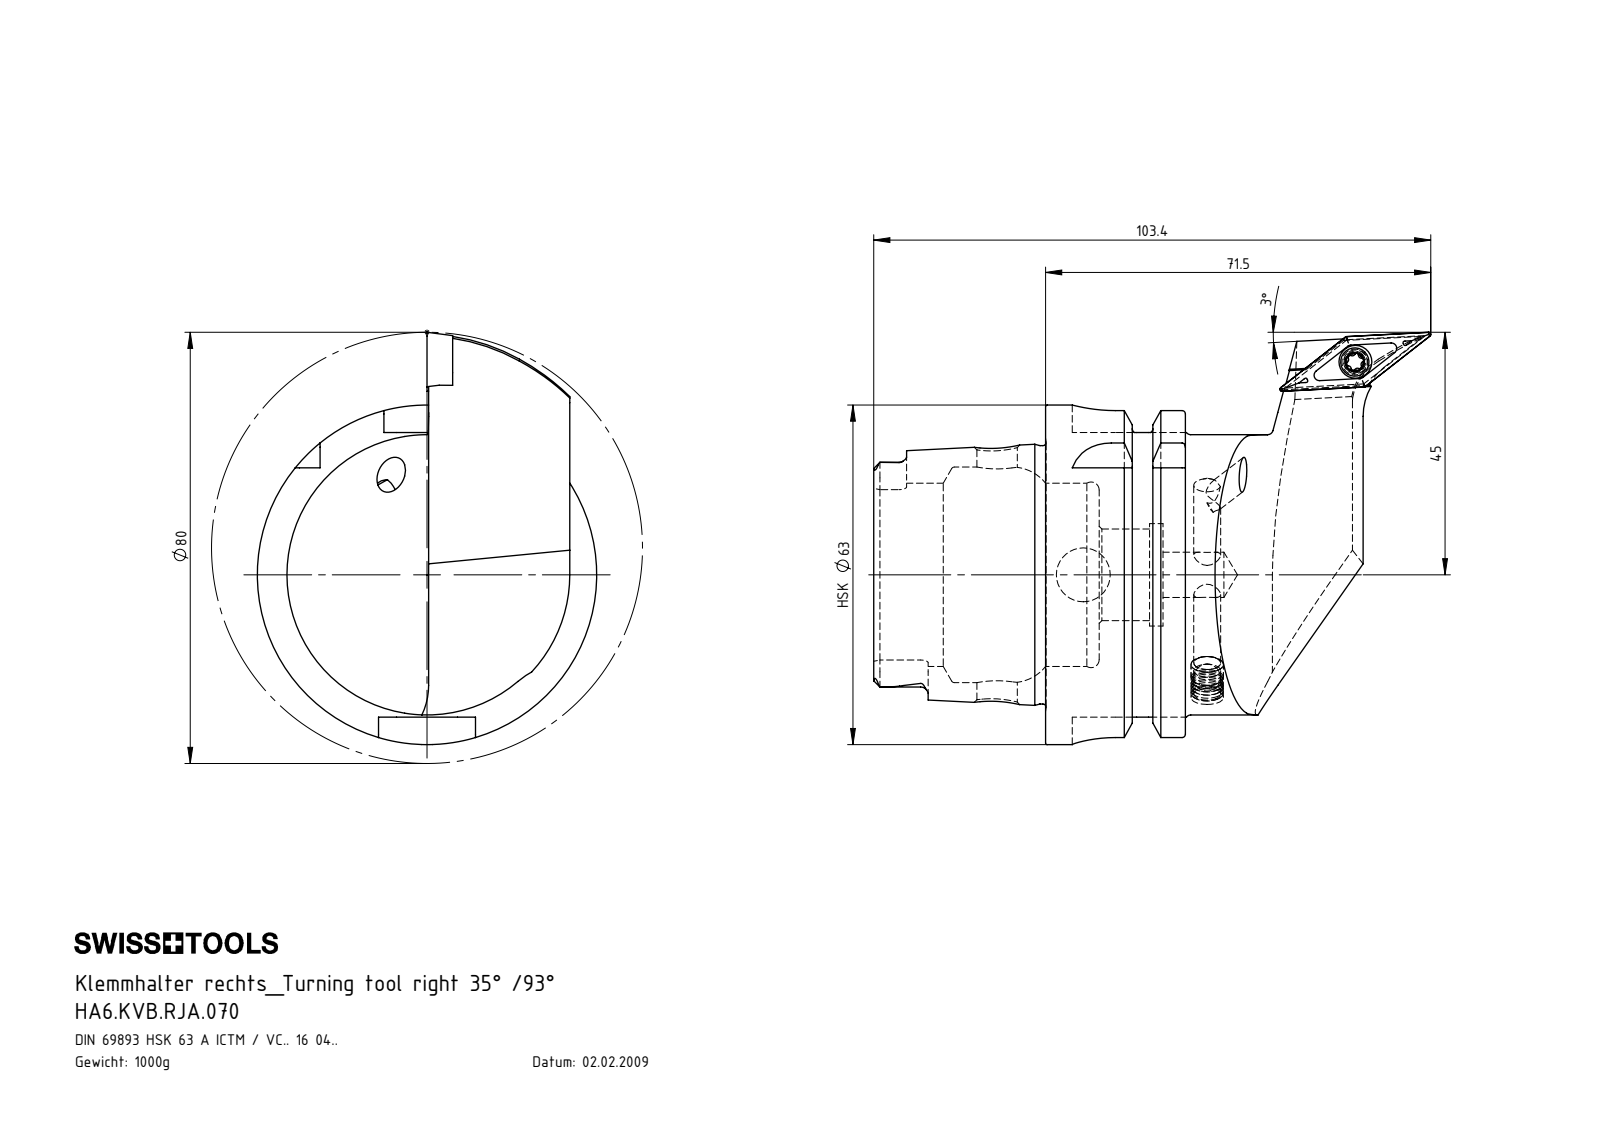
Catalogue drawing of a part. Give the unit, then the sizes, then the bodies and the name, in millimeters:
Units: millimetres
Overall size (bounding box): 103.4 × 76.5 × 63
Round holes (diameter × count): ⌀5 ×3, ⌀3.3 ×1, ⌀4.4 ×1, ⌀6 ×1, ⌀6.1 ×1, ⌀7.5 ×1, ⌀8.4 ×1, ⌀10 ×1, ⌀17 ×1, ⌀19 ×1, ⌀34 ×1, ⌀40 ×1
Round bosses / shafts (diameter × count): ⌀63 ×1, ⌀54.95 ×1, ⌀52 ×1, ⌀47.94 ×1, ⌀6 ×1, ⌀5.25 ×1, ⌀4 ×1
Partial cylindrical surfaces — rounded edges, fillets, slot ends (radius × count): R0.34 ×6, R0.59 ×6, R1.4 ×6, R8 ×4, R2.82 ×2, R2.88 ×2, R6 ×1, R11 ×1
Main face-to-face distances: 25.95, 16, 9.95, 26.2, 31.9, 41.85, 57.85, 52.8, 21.8, 11.85
Hole centre spacings: 64.02, 64.13
Volume: 126 907 mm³ · Surface area: 29 586 mm²
Bodies: 5 solids, 317 faces (82 planar, 90 cylindrical, 145 other)
Part name (STEP PRODUCT): VCMT160404; HA6.KVB.RJA.070; WCB-ER2.001.009_A; HA6-KVB.RJA.070_B (+1 more)
STEP written by: SolidWorks 2017 (AUTOMOTIVE_DESIGN)
